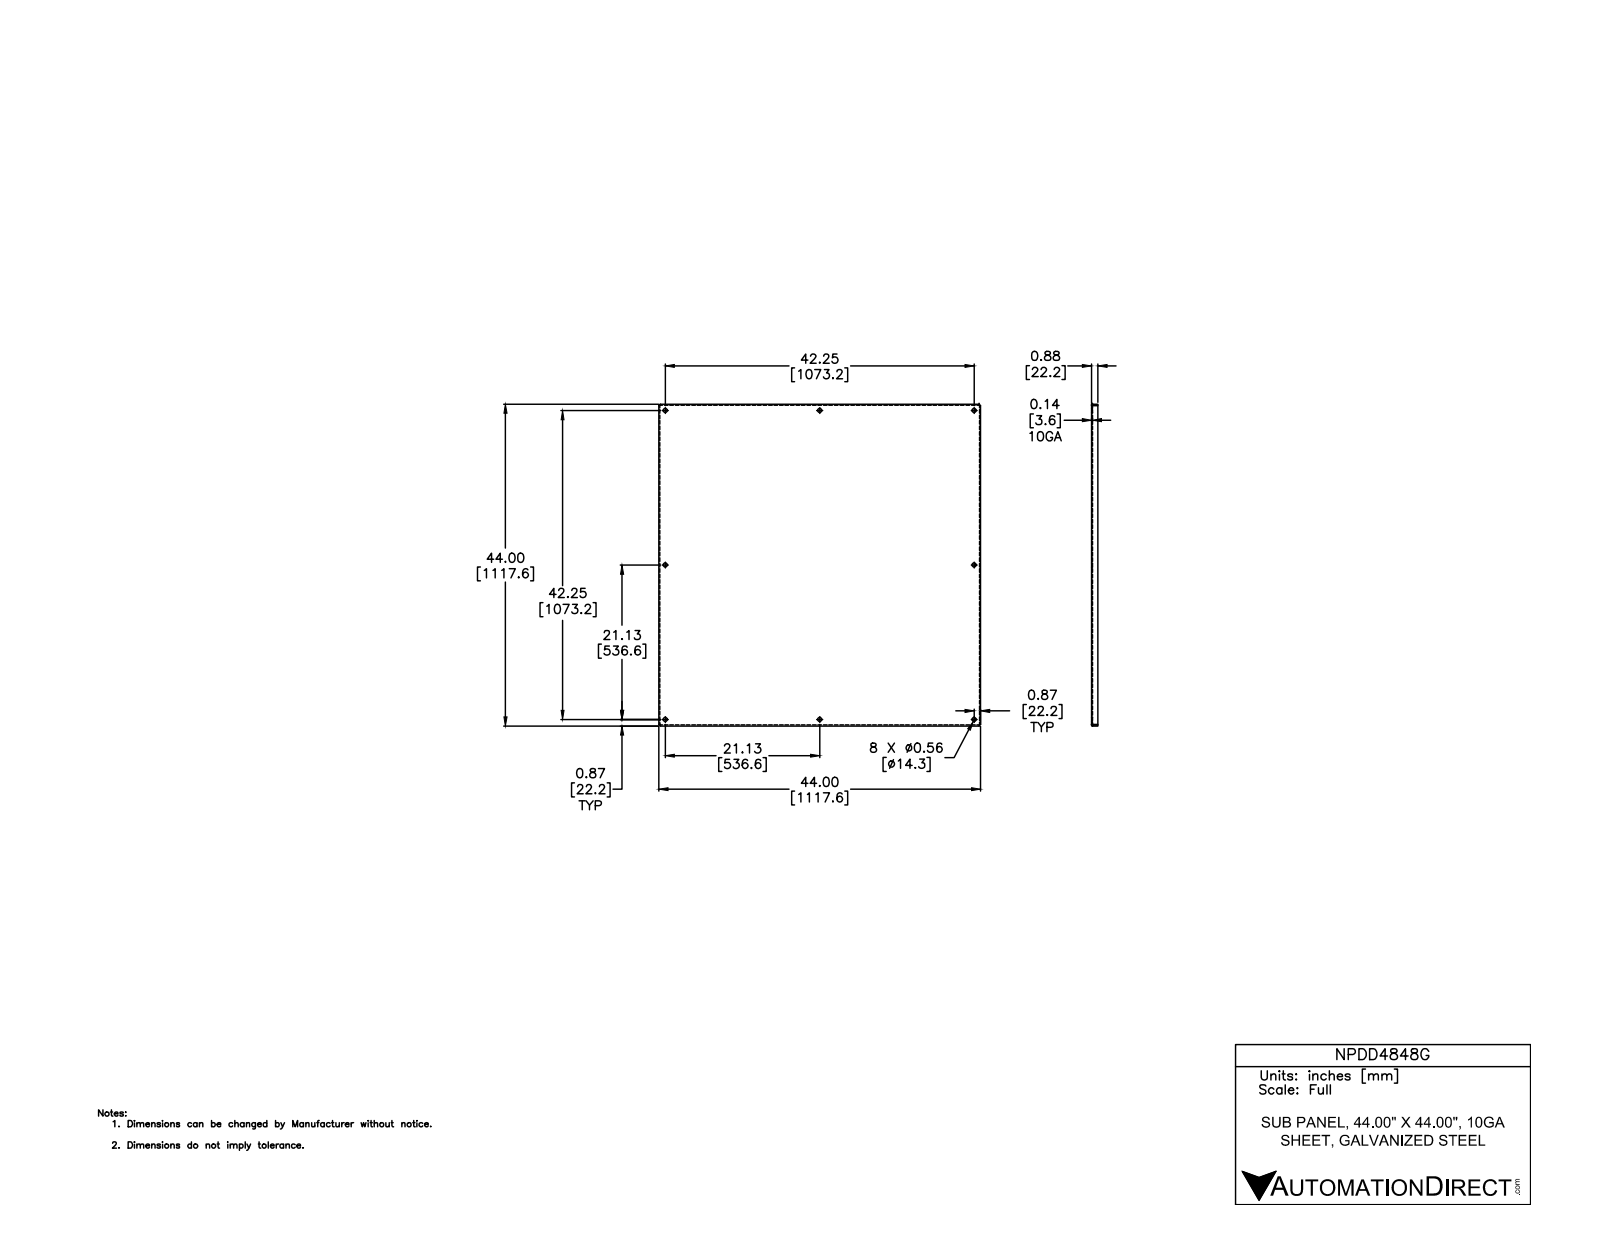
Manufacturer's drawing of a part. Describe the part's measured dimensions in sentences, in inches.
The part is named "NPDD4242G-NPDD7272G". Its 3-D file was written by "Autodesk Inventor 2012 (AUTOMOTIVE_DESIGN)". It is 1 solid with 46 faces: 22 planar, 16 cylindrical and 8 other. Overall it measures 44 by 44 by 0.875 inches. Its volume is 257.2 cubic inches and its surface area 4 140 square inches. Round holes: 8 of diameter 0.563. Partial cylindrical surfaces (rounded edges, fillets, slot ends): 4 of radius 0.031, 4 of radius 0.156. The main face-to-face distances are 0.125, 43.875, 44, 43.75, 0.75, 0.875, 43.787, 43.661, 0.213, 0.088. The hole center spacings are 47.237, 21.125, 42.25, 21.125, 29.875, 42.25, 59.751, 29.875.
